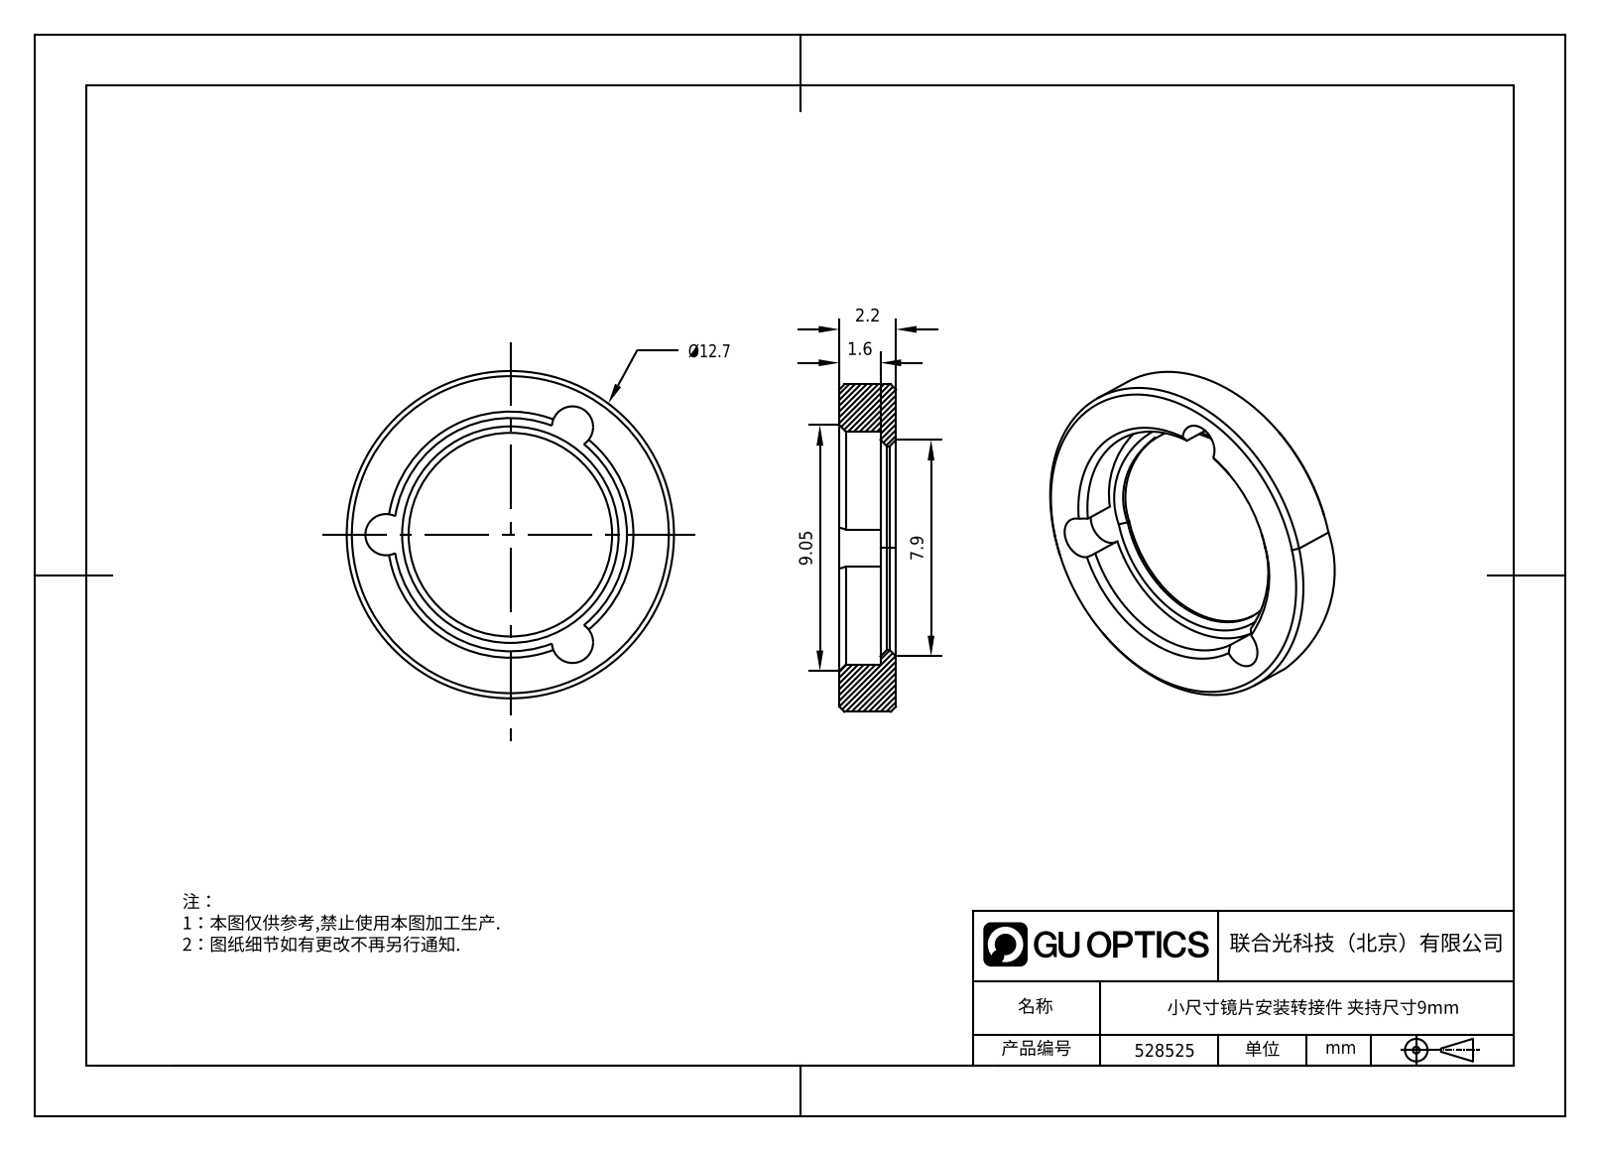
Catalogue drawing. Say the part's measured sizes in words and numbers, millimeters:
The part is named "1.6.4.11-ZSJ-05-9". Its 3-D file was written by "SolidWorks 2021 (CONFIG_CONTROL_DESIGN)". It is 1 solid with 28 faces: 3 planar, 13 cylindrical and 12 other. Overall it measures 12.7 by 12.7 by 2.2 millimeters. Its volume is 135 cubic millimeters and its surface area 292 square millimeters. Round holes: 1 of diameter 7.9, 1 of diameter 9.05. Round bosses or shafts: 1 of diameter 12.7. Partial cylindrical surfaces (rounded edges, fillets, slot ends): 3 of radius 0.8. The main face-to-face distances are 2.2, 0.6, 1.6.
